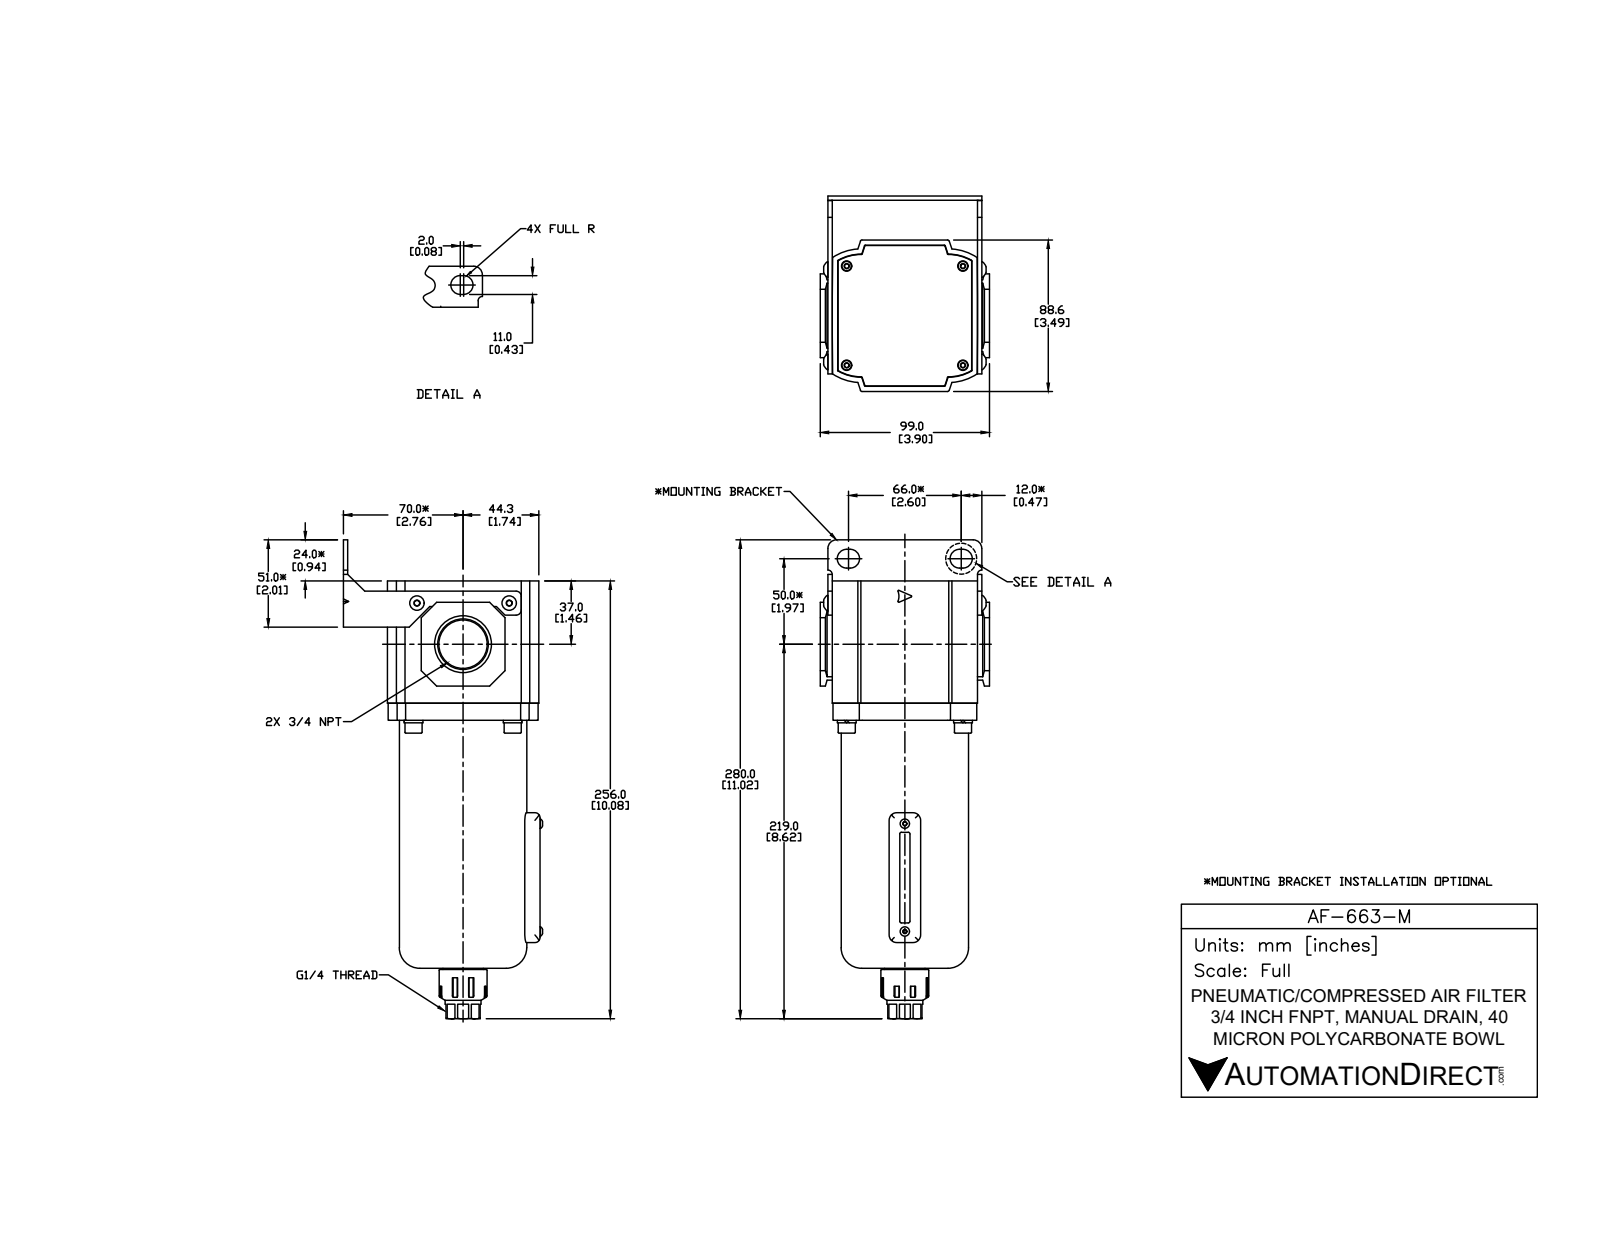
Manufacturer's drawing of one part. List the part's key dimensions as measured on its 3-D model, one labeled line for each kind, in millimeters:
Part name (STEP PRODUCT): AF-663-M
STEP written by: SolidWorks 2015 (CONFIG_CONTROL_DESIGN)
Units: millimetres
Bodies: 8 solids, 384 faces (233 planar, 88 cylindrical, 63 other)
Overall size (bounding box): 280 × 116.49 × 99
Volume: 1 247 000 mm³ · Surface area: 118 905 mm²
Round holes (diameter × count): ⌀5.5 ×2, ⌀11.45 ×1, ⌀23.01 ×1
Round bosses / shafts (diameter × count): ⌀10 ×4, ⌀74.5 ×1, ⌀28 ×1, ⌀21 ×1
Partial cylindrical surfaces — rounded edges, fillets, slot ends (radius × count): R3 ×10, R9.5 ×8, R0.5 ×6, R2 ×5, R0.3 ×4, R1 ×4, R5.5 ×4, R29.7 ×4
Main face-to-face distances: 2.5, 71.5, 85, 92, 25.7, 23.2, 114.3, 111.8, 88.6, 94.5
Hole centre spacings: 36.12, 54
